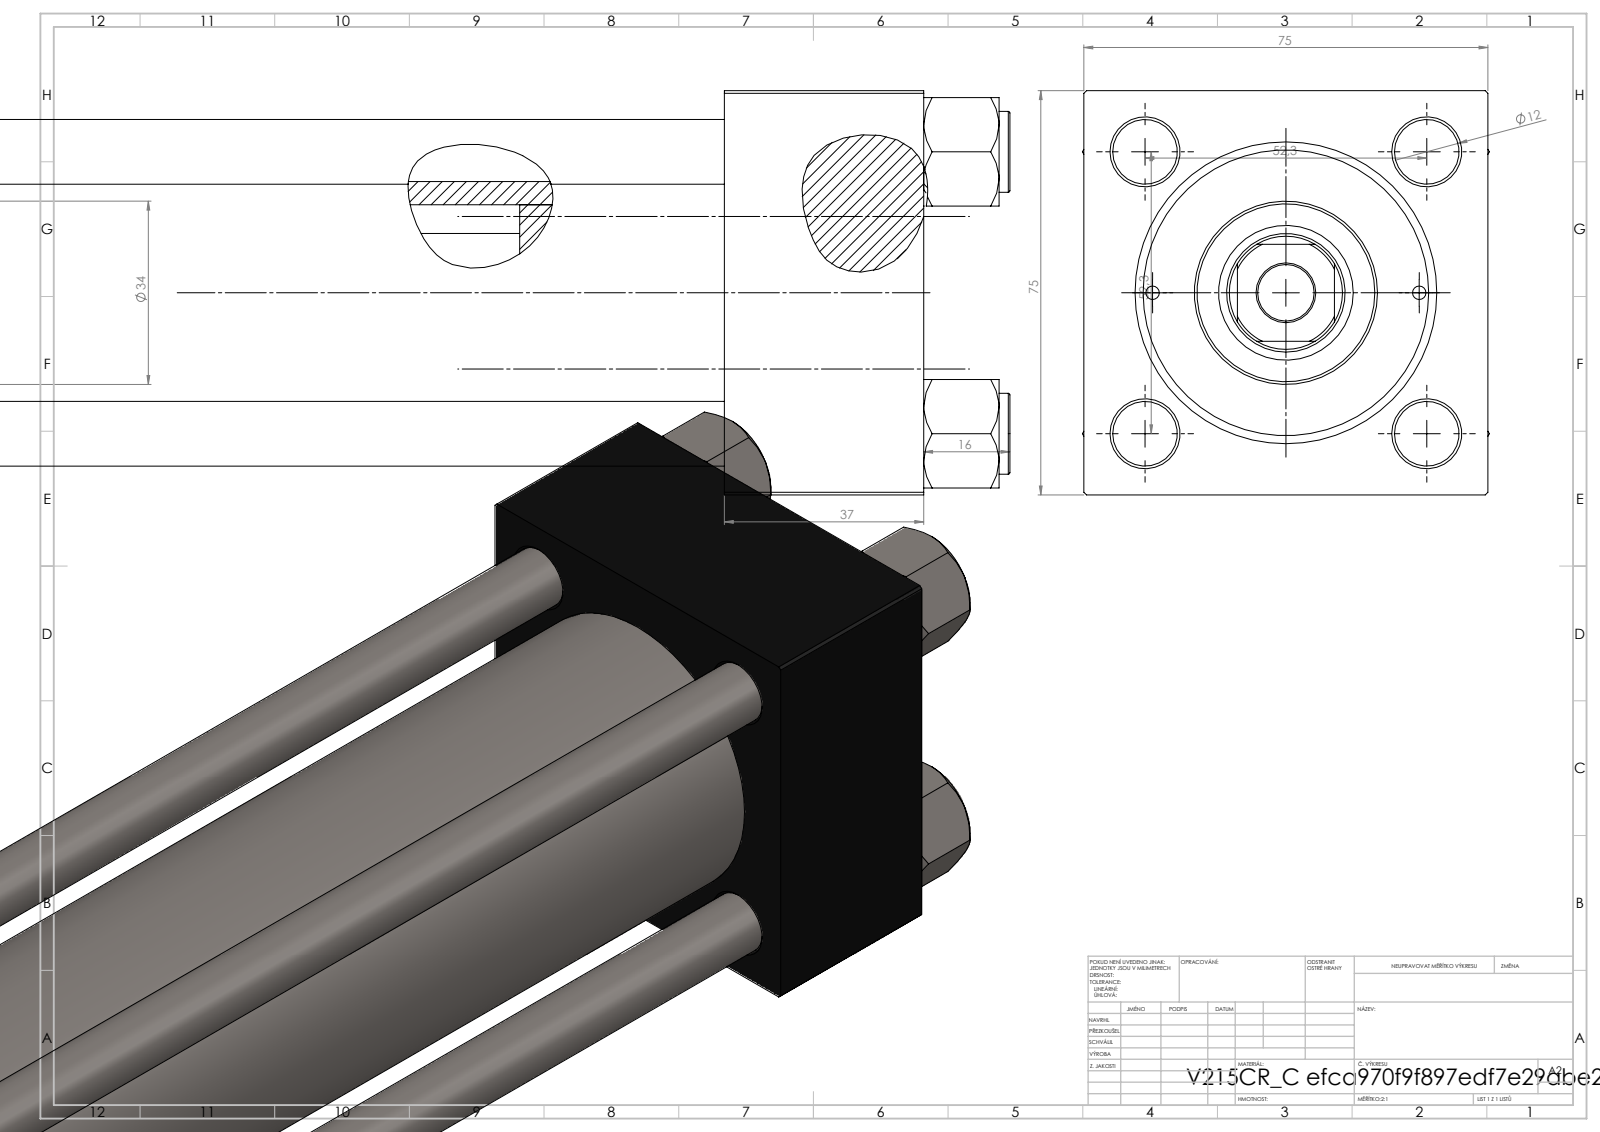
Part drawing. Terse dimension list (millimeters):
name: V215CR_VCP_C; V215_VC_A; V215CR_C_Body; V215CR_C_TYCINKA (+1 more)
written by: SolidWorks 2019 (CONFIG_CONTROL_DESIGN)
unit: mm
bodies: 11 solids, 1154 faces (528 planar, 90 cylindrical, 536 other)
size: 525 × 75.54 × 75
volume: 1 096 000 mm³; area: 329 828 mm²
holes: 4× ⌀12, 2× ⌀2.5, 2× ⌀7, 2× ⌀20.96, 2× ⌀30, 1× ⌀10.5, 1× ⌀22, 1× ⌀25, 1× ⌀41, 1× ⌀50, 1× ⌀53
bosses: 4× ⌀15, 1× ⌀56, 1× ⌀34
rounds: 1× R10.5
face distances: 75, 37, 484, 447, 425, 388, 59, 455.3, 418.3, 30.3
hole spacings: 26.19, 36.98, 52.3, 57.22, 24.75, 73.96, 49.5, 423.5
